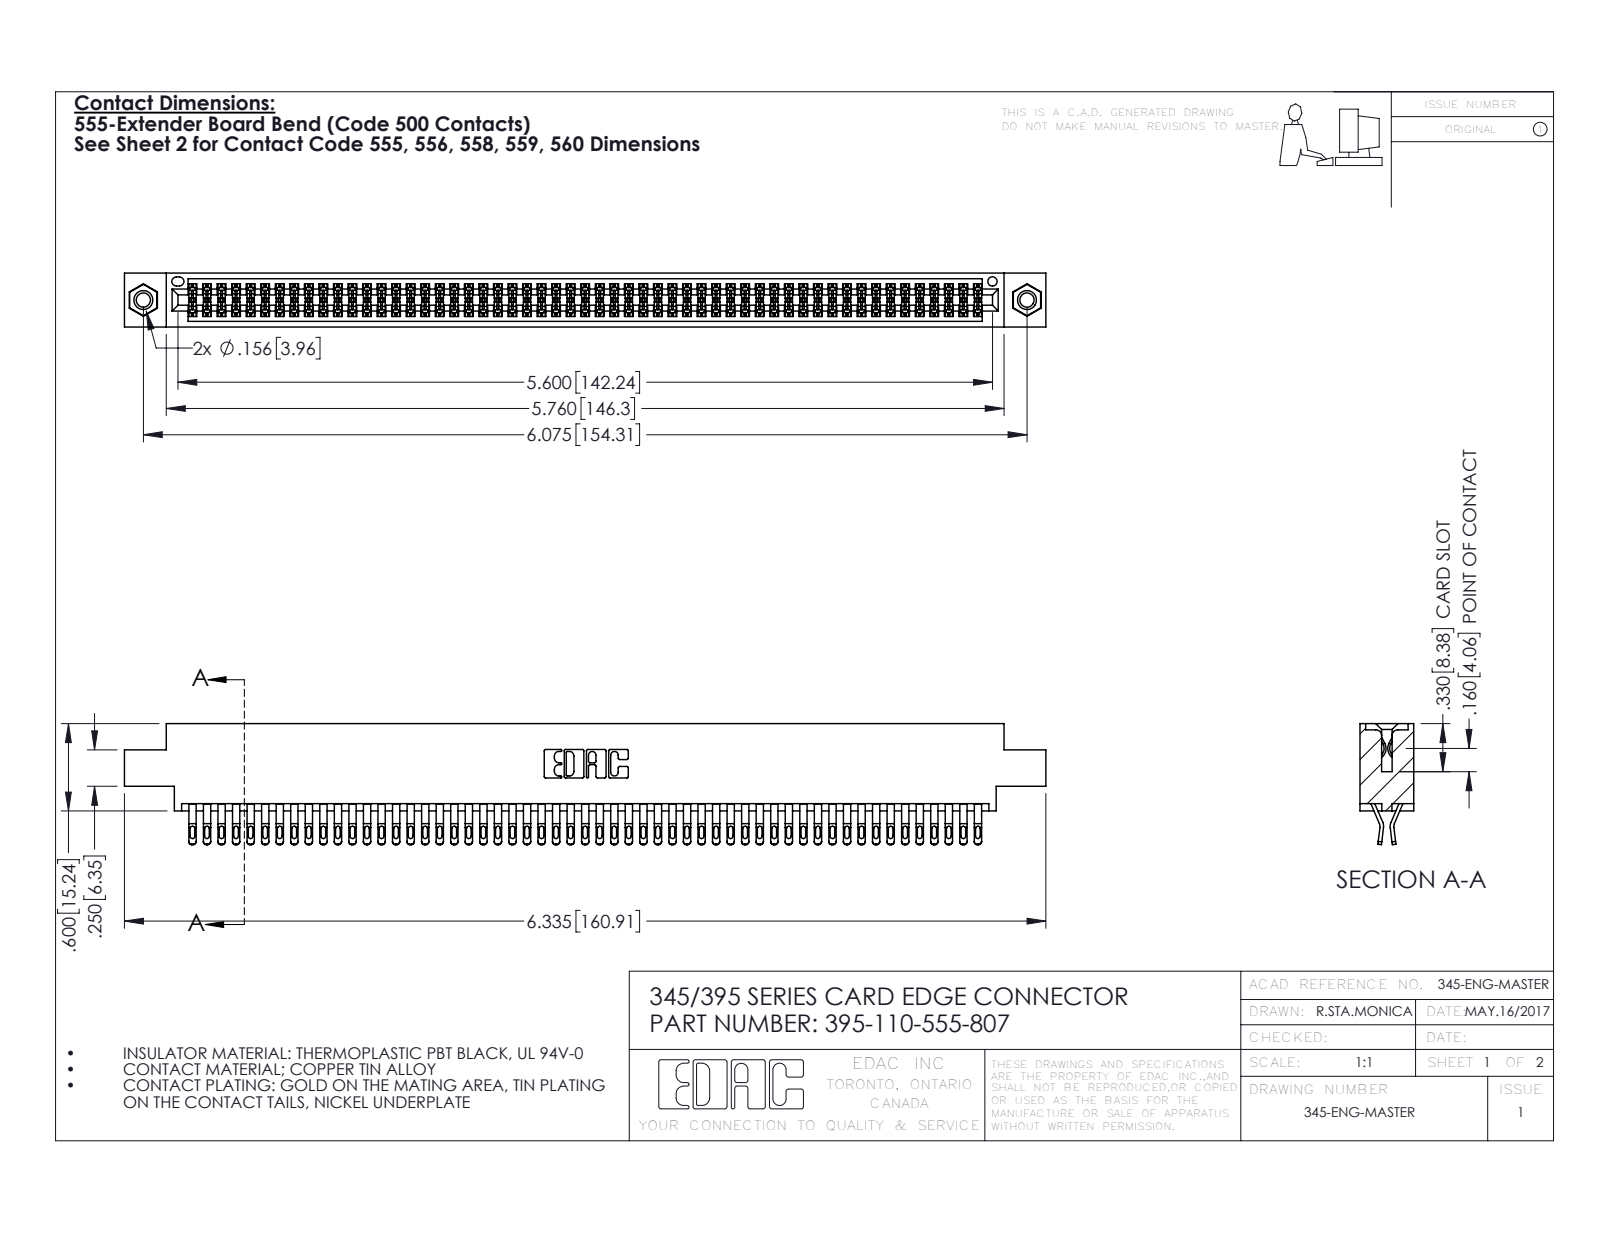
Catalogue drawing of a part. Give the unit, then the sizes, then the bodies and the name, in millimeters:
Units: millimetres
Overall size (bounding box): 160.9 × 21.1 × 9.4
Round holes (diameter × count): ⌀2.5 ×2, ⌀3.2 ×2, ⌀4 ×2, ⌀1.6 ×1
Round bosses / shafts (diameter × count): ⌀3.9 ×2
Partial cylindrical surfaces — rounded edges, fillets, slot ends (radius × count): R0.4 ×275, R0.5 ×220, R0.2 ×165, R0.3 ×22, R0.2 ×6, R0.8 ×6, R0.7 ×3, R0.3 ×2
Main face-to-face distances: 1.8, 7.6, 9.4, 0.6, 5.1, 2.5, 6.9, 5.7, 4.4, 3.8
Hole centre spacings: 6.9, 148.3, 154.3
Volume: 15 900 mm³ · Surface area: 25 100 mm²
Bodies: 113 solids, 6350 faces (3526 planar, 2808 cylindrical, 16 other)
Part name (STEP PRODUCT): 345 Part_0.170 Offset - 0.156 Dia-TI; 395-110-555-807; 345-250-001_345-250-005-103; 345-292-001_555 Tail
STEP written by: SolidWorks 2016 (CONFIG_CONTROL_DESIGN)
